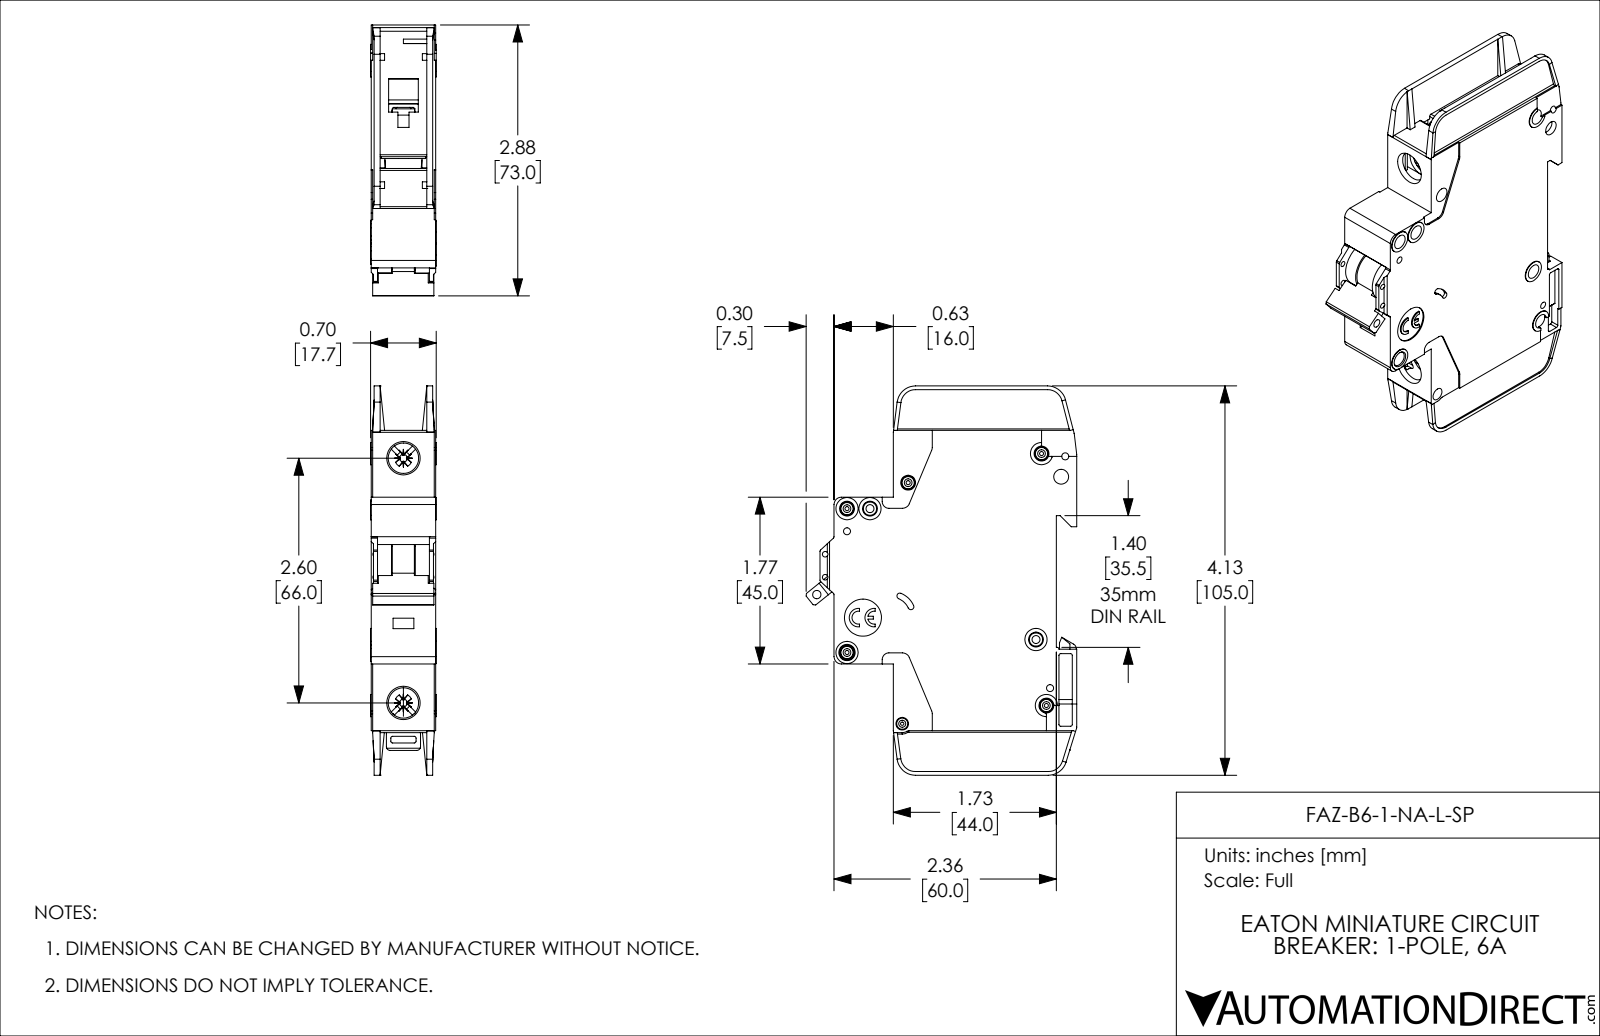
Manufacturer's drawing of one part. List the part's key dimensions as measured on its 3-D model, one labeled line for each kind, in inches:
Part name (STEP PRODUCT): FAZ-B6-1-NA-L-SP
STEP written by: SolidWorks 2019 (AUTOMOTIVE_DESIGN)
Units: inches
Bodies: 1 solid, 1127 faces (671 planar, 357 cylindrical, 99 other)
Overall size (bounding box): 4.134 × 2.876 × 0.697
Volume: 4.682 in³ · Surface area: 41.01 in²
Round holes (diameter × count): ⌀0.157 ×8, ⌀0.043 ×5, ⌀0.075 ×4, ⌀0.059 ×2, ⌀0.085 ×2, ⌀0.323 ×2, ⌀0.035 ×1, ⌀0.089 ×1, ⌀0.098 ×1, ⌀0.134 ×1, ⌀0.394 ×1
Round bosses / shafts (diameter × count): ⌀0.13 ×5, ⌀0.236 ×4, ⌀0.118 ×2, ⌀0.098 ×1
Partial cylindrical surfaces — rounded edges, fillets, slot ends (radius × count): R0.02 ×42, R0.016 ×10, R0.039 ×10, R0.079 ×8, R0.197 ×5, R0.008 ×4, R0.026 ×4, R0.043 ×4
Main face-to-face distances: 0.047, 0.685, 0.591, 0.638, 0.094, 0.543, 0.016, 0.031, 0.496, 0.575
Hole centre spacings: 0.244, 0.537, 0.87, 0.189, 0.199, 0.204, 0.221, 0.24
